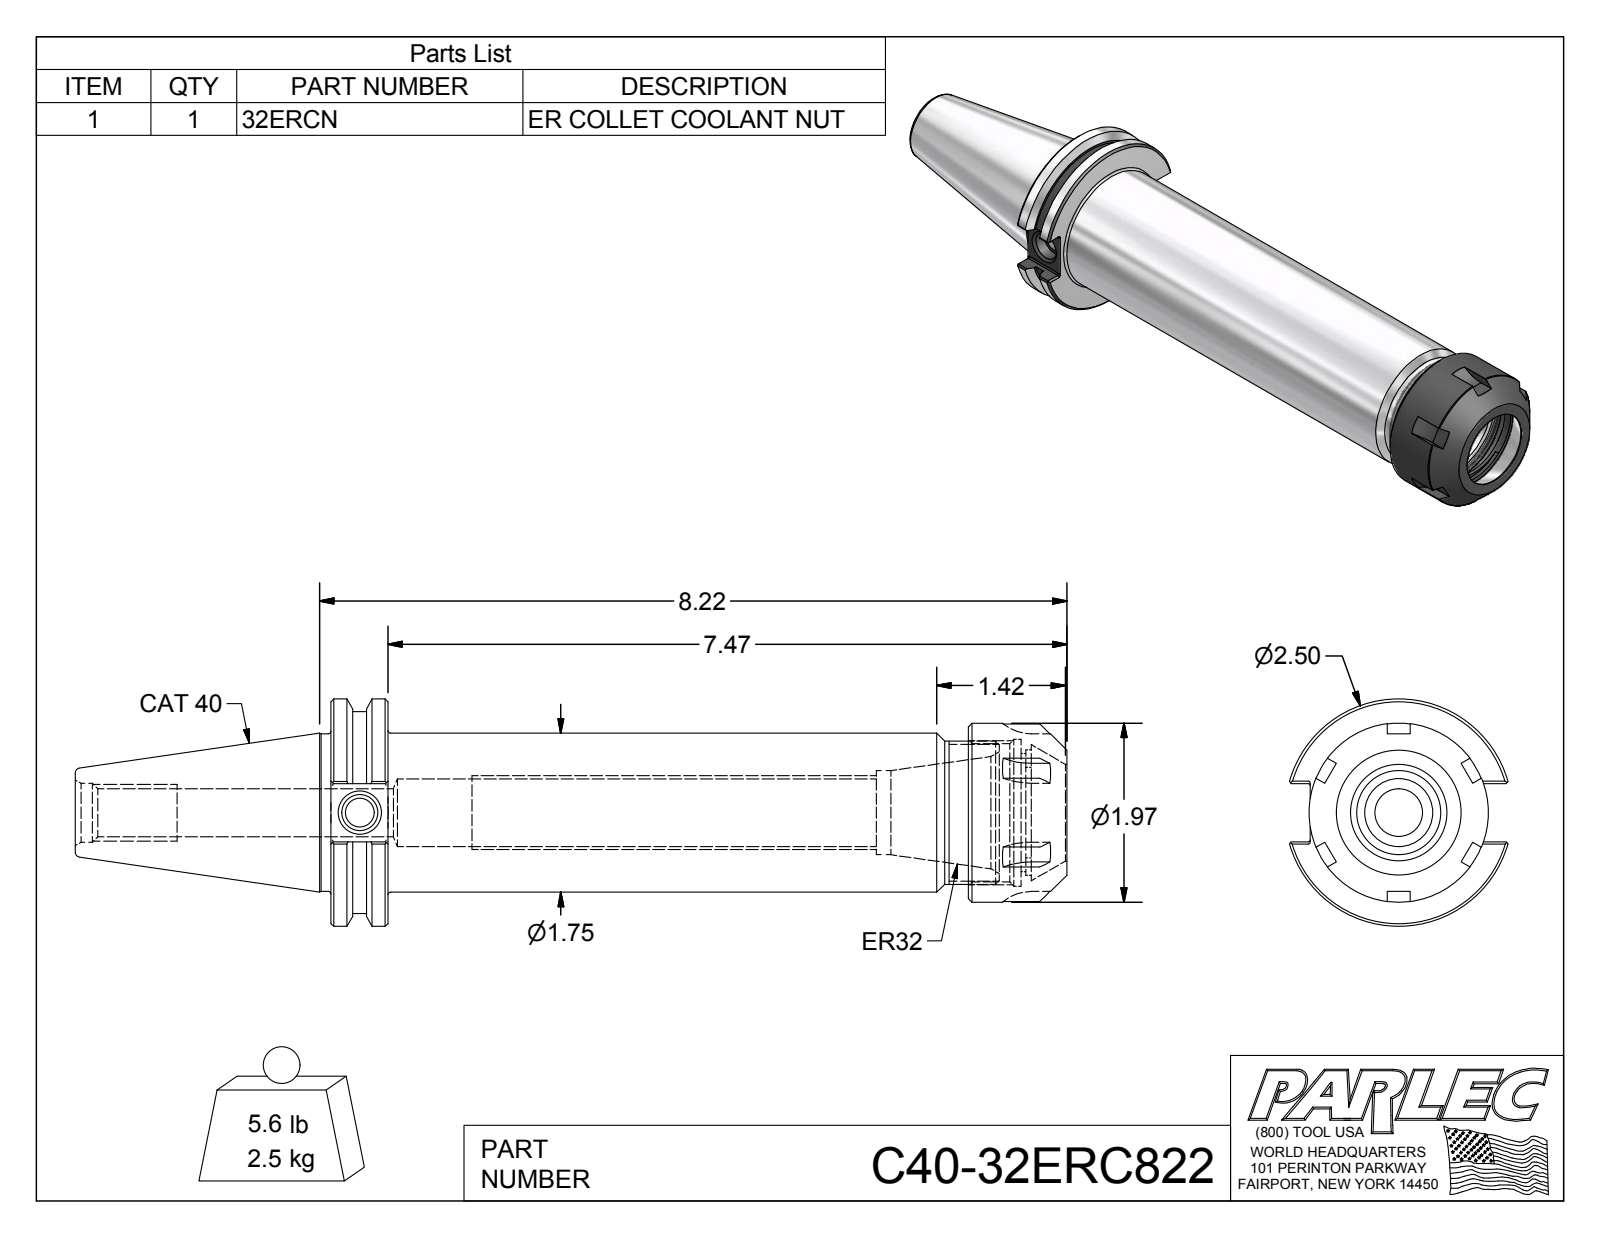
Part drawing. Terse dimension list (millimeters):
name: C40-32ERC822; C40-32ER8-1; 32ERCN
written by: Autodesk Inventor 2012 (AUTOMOTIVE_DESIGN)
unit: mm
bodies: 2 solids, 127 faces (55 planar, 39 cylindrical, 33 other)
size: 277.1 × 63.5 × 61
volume: 322 500 mm³; area: 64 010 mm²
holes: 1× ⌀8, 1× ⌀10.1, 1× ⌀13.4, 1× ⌀16.5, 1× ⌀18.9, 1× ⌀23.5, 1× ⌀27, 1× ⌀33, 1× ⌀38.7, 1× ⌀41
bosses: 1× ⌀63.5, 1× ⌀56.4, 1× ⌀50, 1× ⌀44.5, 1× ⌀43.9, 1× ⌀40
rounds: 12× R0.5, 6× R12.7, 1× R17.5
face distances: 15.9, 178.1, 162.2, 192.8, 176.9, 14.7, 205.6, 189.7, 27.5, 12.8
hole spacings: 1.5
